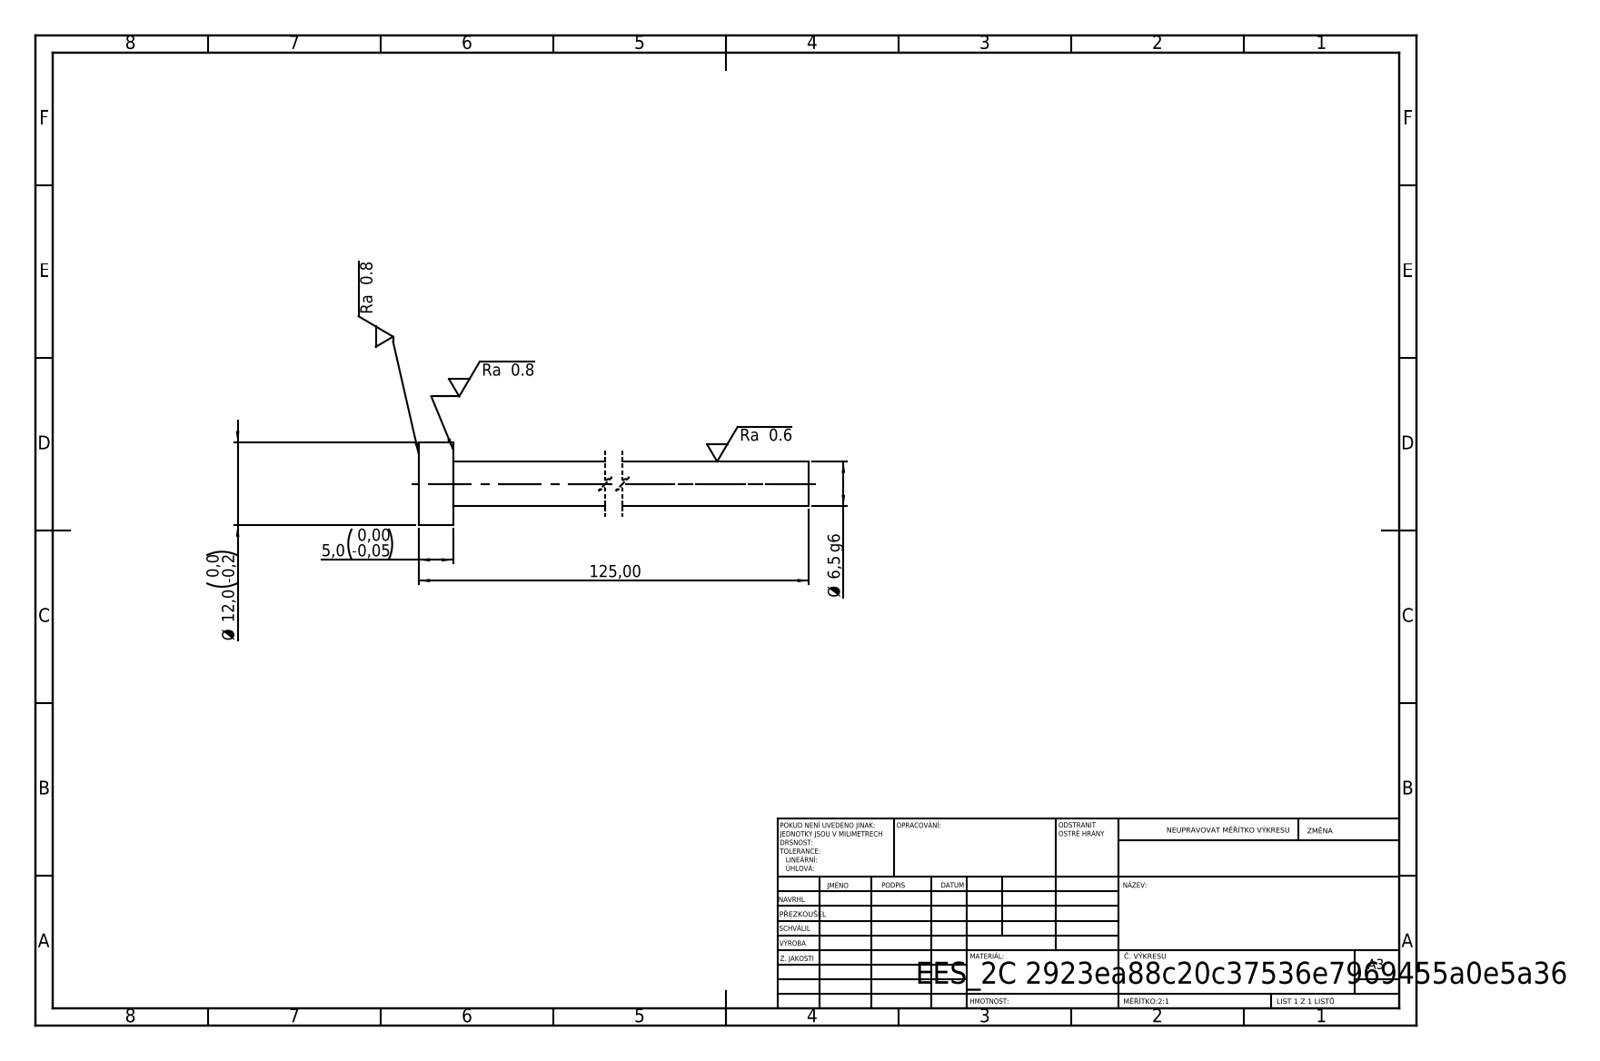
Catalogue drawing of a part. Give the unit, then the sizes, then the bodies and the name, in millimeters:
Units: millimetres
Overall size (bounding box): 125 × 12 × 12
Round bosses / shafts (diameter × count): ⌀12 ×1, ⌀6.5 ×1
Main face-to-face distances: 5, 125, 120
Volume: 4 547 mm³ · Surface area: 2 865 mm²
Bodies: 1 solid, 7 faces (3 planar, 4 cylindrical, 0 other)
STEP written by: SolidWorks 2019 (CONFIG_CONTROL_DESIGN)
